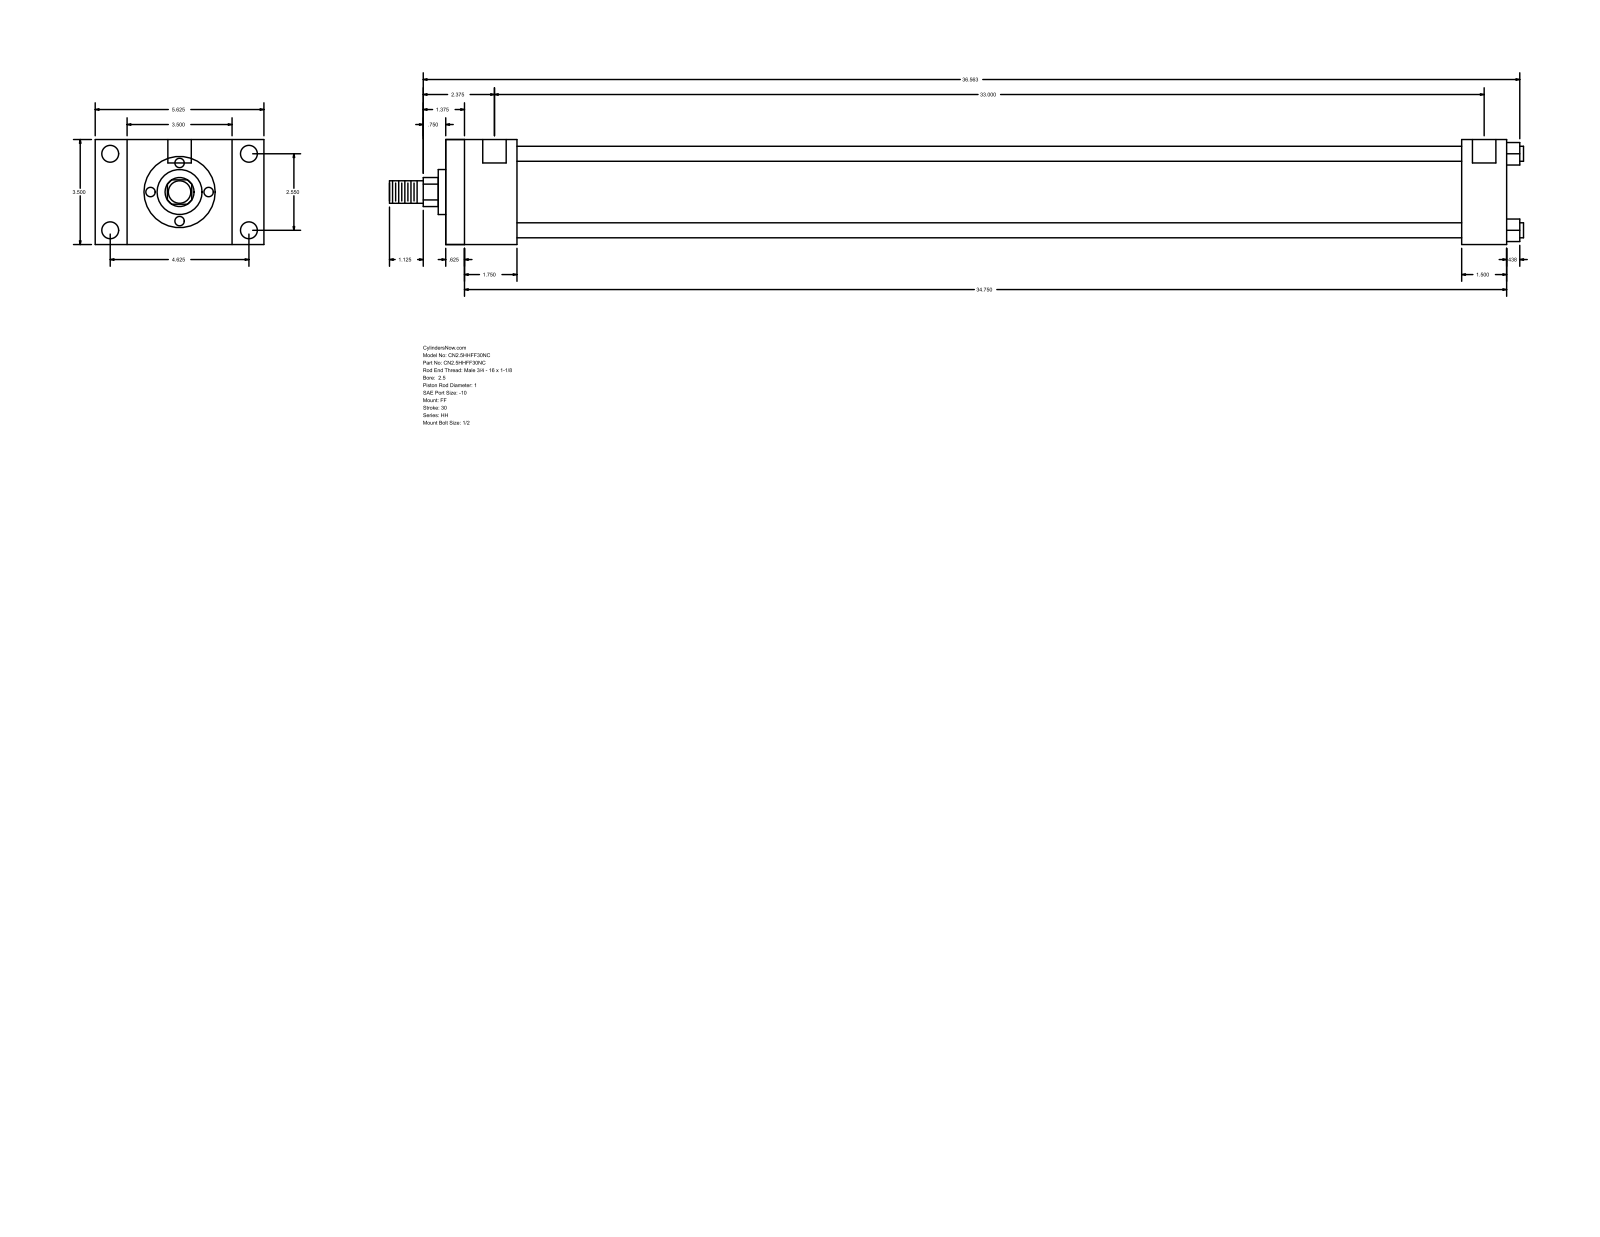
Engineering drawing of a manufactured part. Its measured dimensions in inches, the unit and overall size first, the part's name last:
Units: inches
Overall size (bounding box): 37.813 × 5.625 × 3.5
Round holes (diameter × count): ⌀0.219 ×4, ⌀0.563 ×4, ⌀0.781 ×2
Round bosses / shafts (diameter × count): ⌀0.5 ×4, ⌀2.875 ×1, ⌀1.5 ×1, ⌀1 ×1, ⌀0.75 ×1
Partial cylindrical surfaces — rounded edges, fillets, slot ends (radius × count): R0.484 ×1
Main face-to-face distances: 3.5, 35.375, 0.625, 34.75, 1.5, 2.375, 1.75, 33, 33.875, 33.25
Hole centre spacings: 0.063, 2.55, 4.625, 5.281, 33.062, 33.125, 33
Bodies: 0 solids, 92 faces (64 planar, 28 cylindrical, 0 other)
Part name (STEP PRODUCT): HH_FF__0250_1
STEP written by: GSSL Pune (CONFIG_CONTROL_DESIGN)
